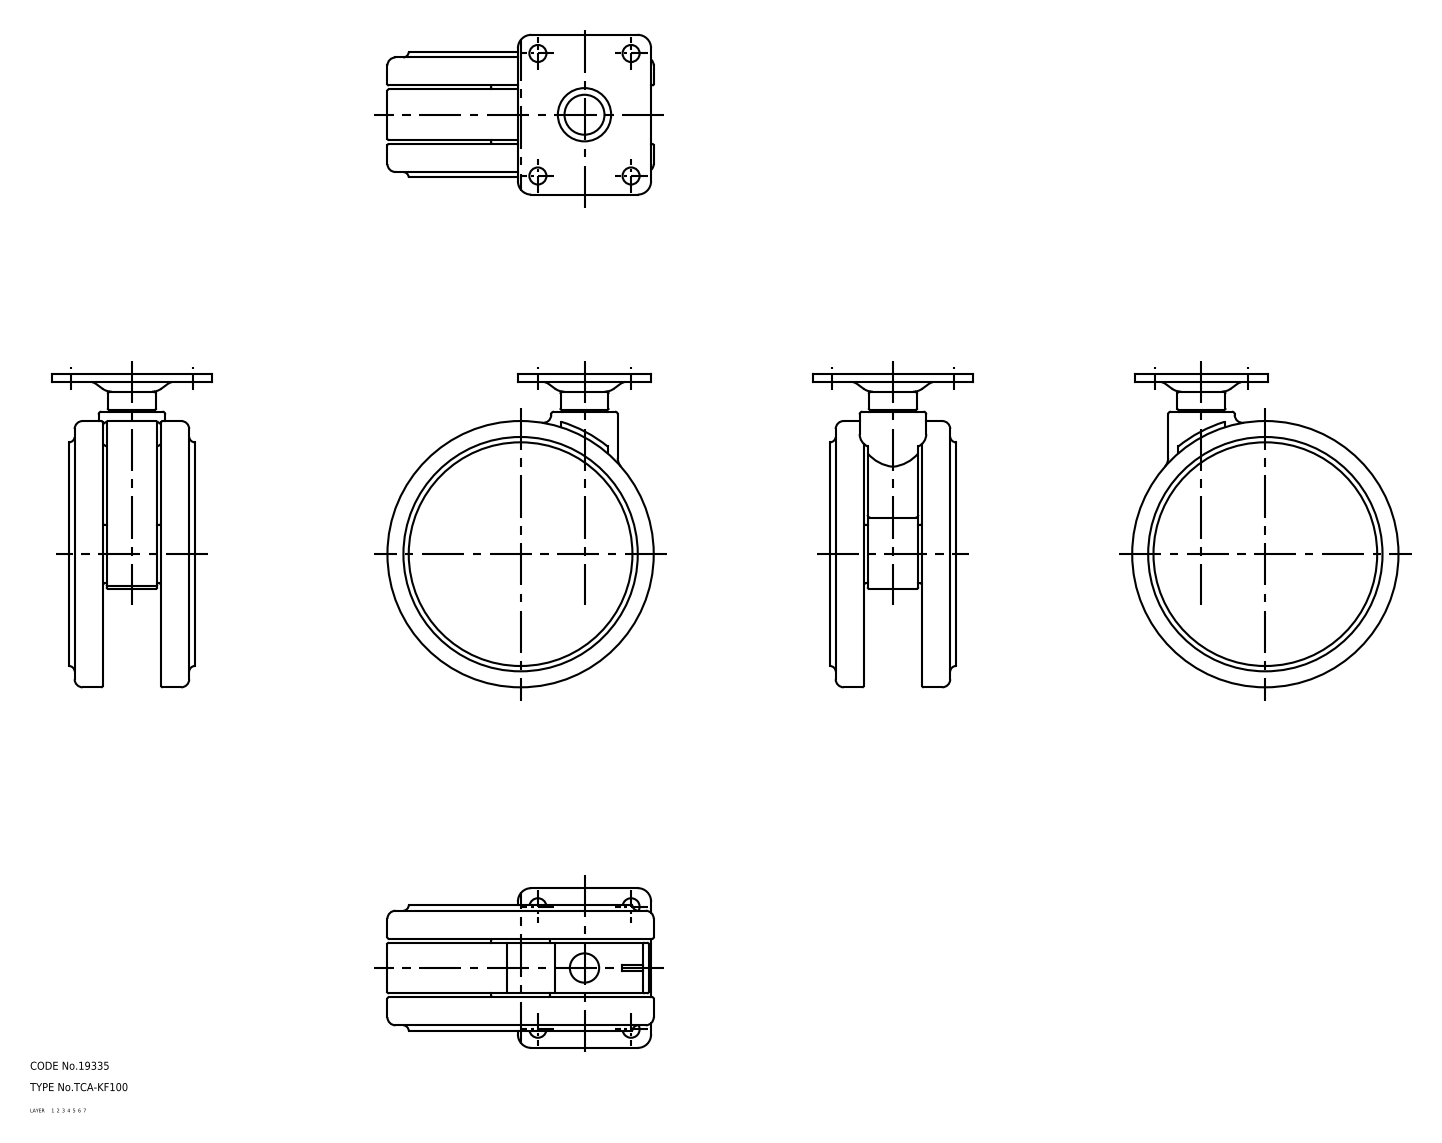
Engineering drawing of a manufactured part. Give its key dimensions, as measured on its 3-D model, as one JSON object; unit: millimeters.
{"part_name": "main shaft; wheel_mr; mounting plate; wheel (+1 more)", "step_written_by": "SolidWorks 2015 (AUTOMOTIVE_DESIGN)", "units": "millimeters", "bodies": {"solids": 5, "faces": 155, "planar": 33, "cylindrical": 60, "other": 62}, "overall_size": [117.5, 100, 60], "volume_mm3": 242600, "surface_area_mm2": 63806, "round_holes": [[6.4, 4], [6, 1], [72, 1]], "round_bosses_or_shafts": [[100, 1], [25, 1], [22, 1], [18, 1], [17, 1], [15, 1]], "partial_cylinders_radius": [[0.5, 12], [5, 4], [1, 1], [13, 1], [48.08, 1], [52, 1]], "face_to_face_distances": [14, 33, 20.5, 1.5, 12.5, 34.5, 6.5, 39.5, 7.5, 5], "hole_center_spacings": [28.9, 35, 46, 57.8]}
